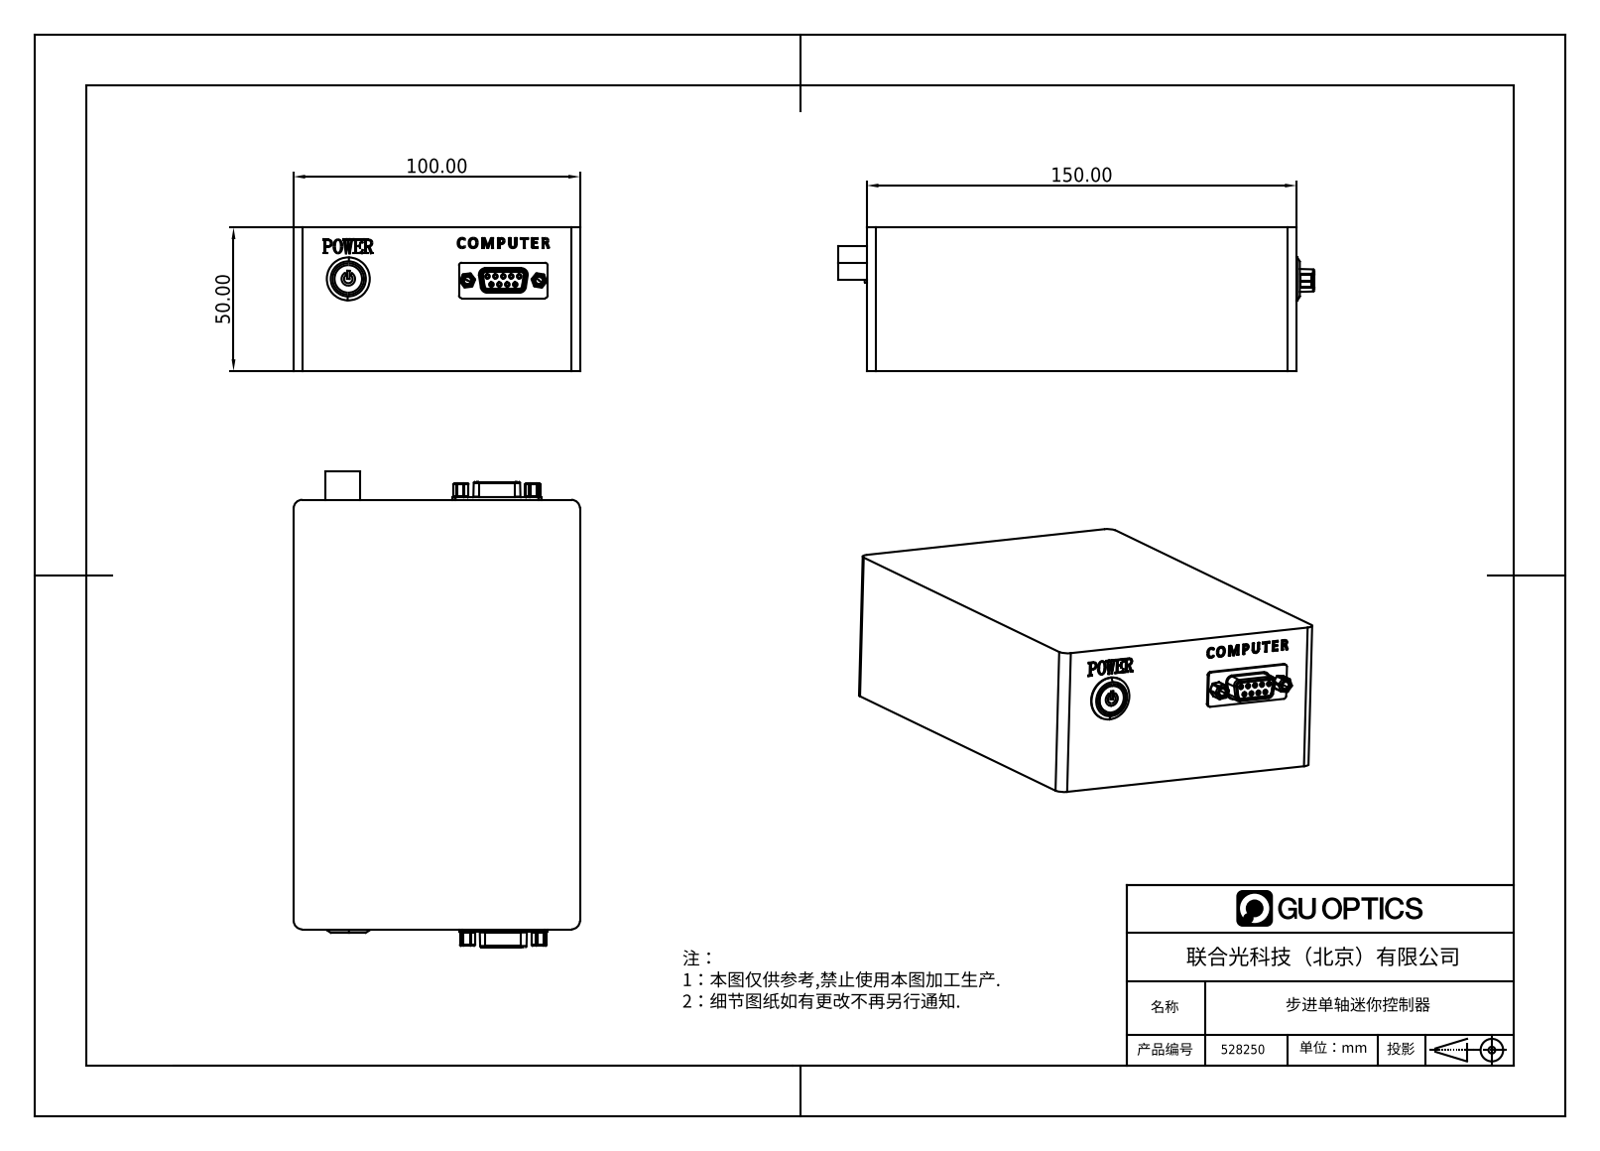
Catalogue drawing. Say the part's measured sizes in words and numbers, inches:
The part is named "零件6^528250". Its 3-D file was written by "SolidWorks 2020 (CONFIG_CONTROL_DESIGN)". It is 19 solids with 1385 faces: 558 planar, 424 cylindrical and 403 other. Overall it measures 6.547 by 3.937 by 1.969 inches. Its volume is 44.84 cubic inches and its surface area 112.6 square inches. Round holes: 28 of diameter 0.091, 20 of diameter 0.039, 18 of diameter 0.043, 8 of diameter 0.098, 4 of diameter 0.126, 4 of diameter 0.157, 1 of diameter 0.185, 1 of diameter 0.432, 1 of diameter 0.433, 1 of diameter 0.543. Round bosses or shafts: 18 of diameter 0.059, 5 of diameter 0.118, 1 of diameter 0.591, 1 of diameter 0.472, 1 of diameter 0.42, 1 of diameter 0.378, 1 of diameter 0.359, 1 of diameter 0.236. Partial cylindrical surfaces (rounded edges, fillets, slot ends): 80 of radius 0.02, 16 of radius 0.012, 16 of radius 0.039, 8 of radius 0.036, 8 of radius 0.039, 8 of radius 0.051, 8 of radius 0.055, 8 of radius 0.055. The main face-to-face distances are 1.969, 3.937, 5.906, 0.551, 0.787, 5.118, 0.213, 0.236, 0.968, 1.519. The hole center spacings are 0.124, 0.109, 0.495, 0.589, 0.636, 0.218, 0.296, 0.561.
